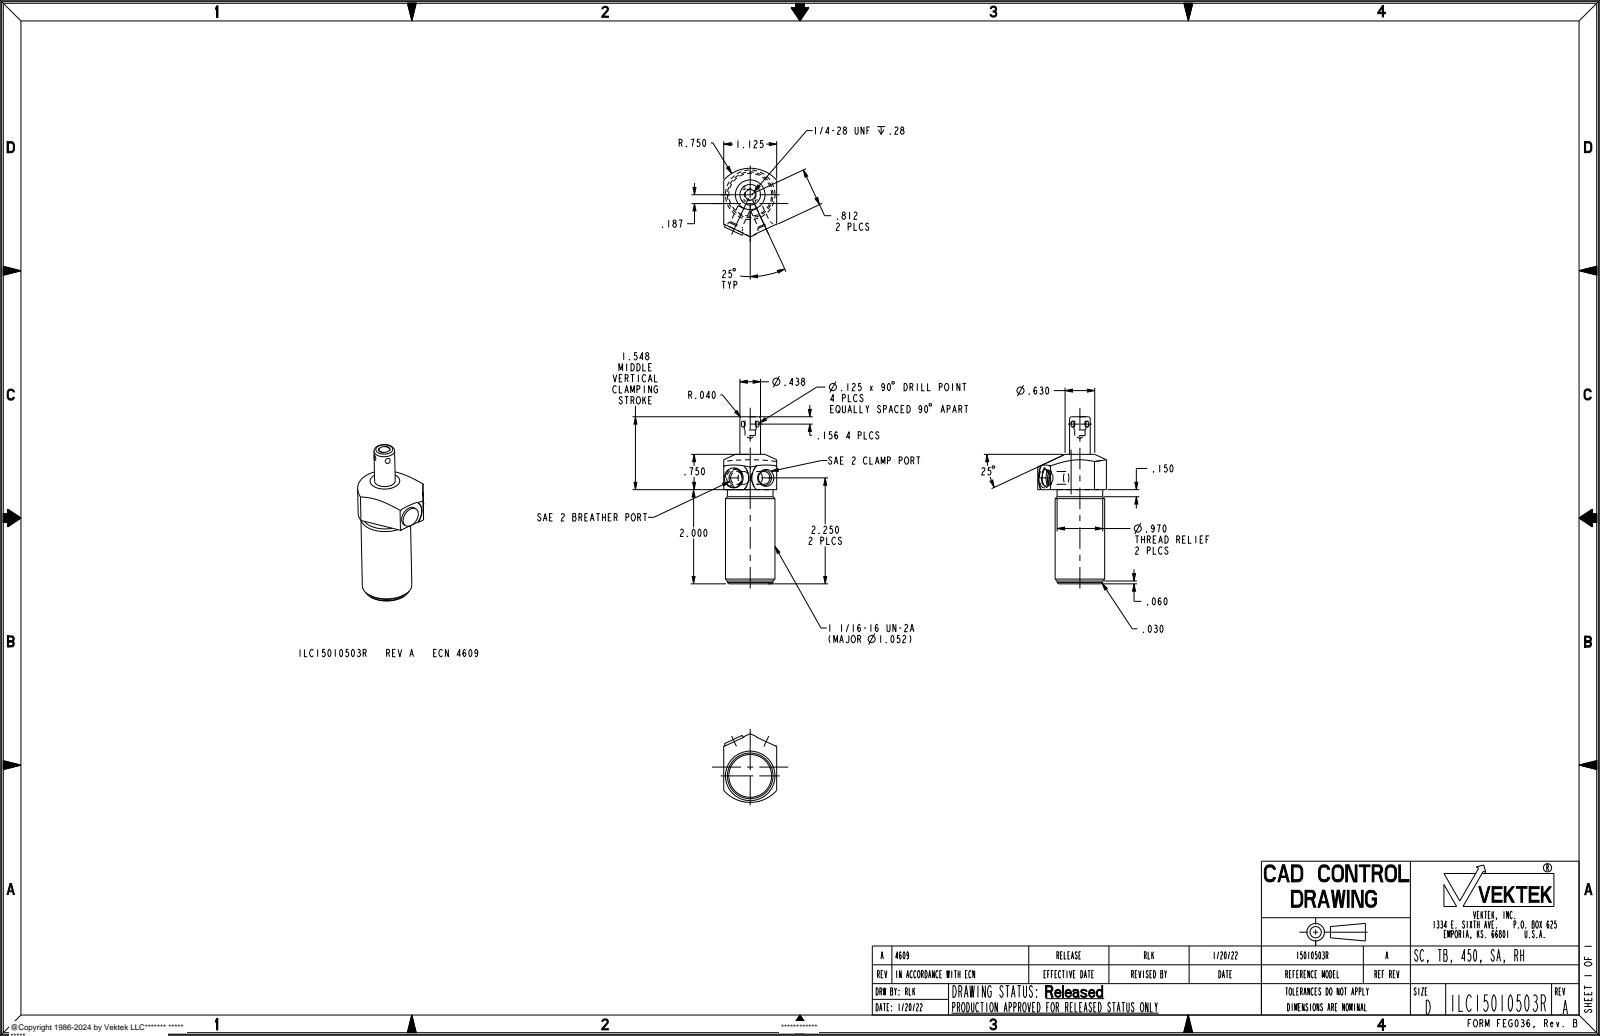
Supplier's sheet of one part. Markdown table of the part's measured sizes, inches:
| quantity | value |
| --- | --- |
| part name | ILC15010503R |
| STEP written by | CREO PARAMETRIC BY PTC INC, 2021164 (AUTOMOTIVE_DESIGN) |
| units | inches |
| bodies | 1 solid, 72 faces (19 planar, 25 cylindrical, 28 other) |
| overall size | 3.548 × 1.459 × 1.125 |
| volume | 2.688 in³ |
| surface area | 14.74 in² |
| round holes (diameter × count) | 0.272 × 2, 0.221 × 1 |
| round bosses / shafts (diameter × count) | 1.052 × 1, 0.97 × 1, 0.438 × 1, 0.418 × 1, 0.25 × 1 |
| partial cylindrical surfaces (radius × count) | 0.341 × 2, 0.75 × 1 |
| main face-to-face distances | 2, 1.125, 2.75, 0.75, 0.05, 0.48, 0.05, 3.548, 1.548, 0.798 |
